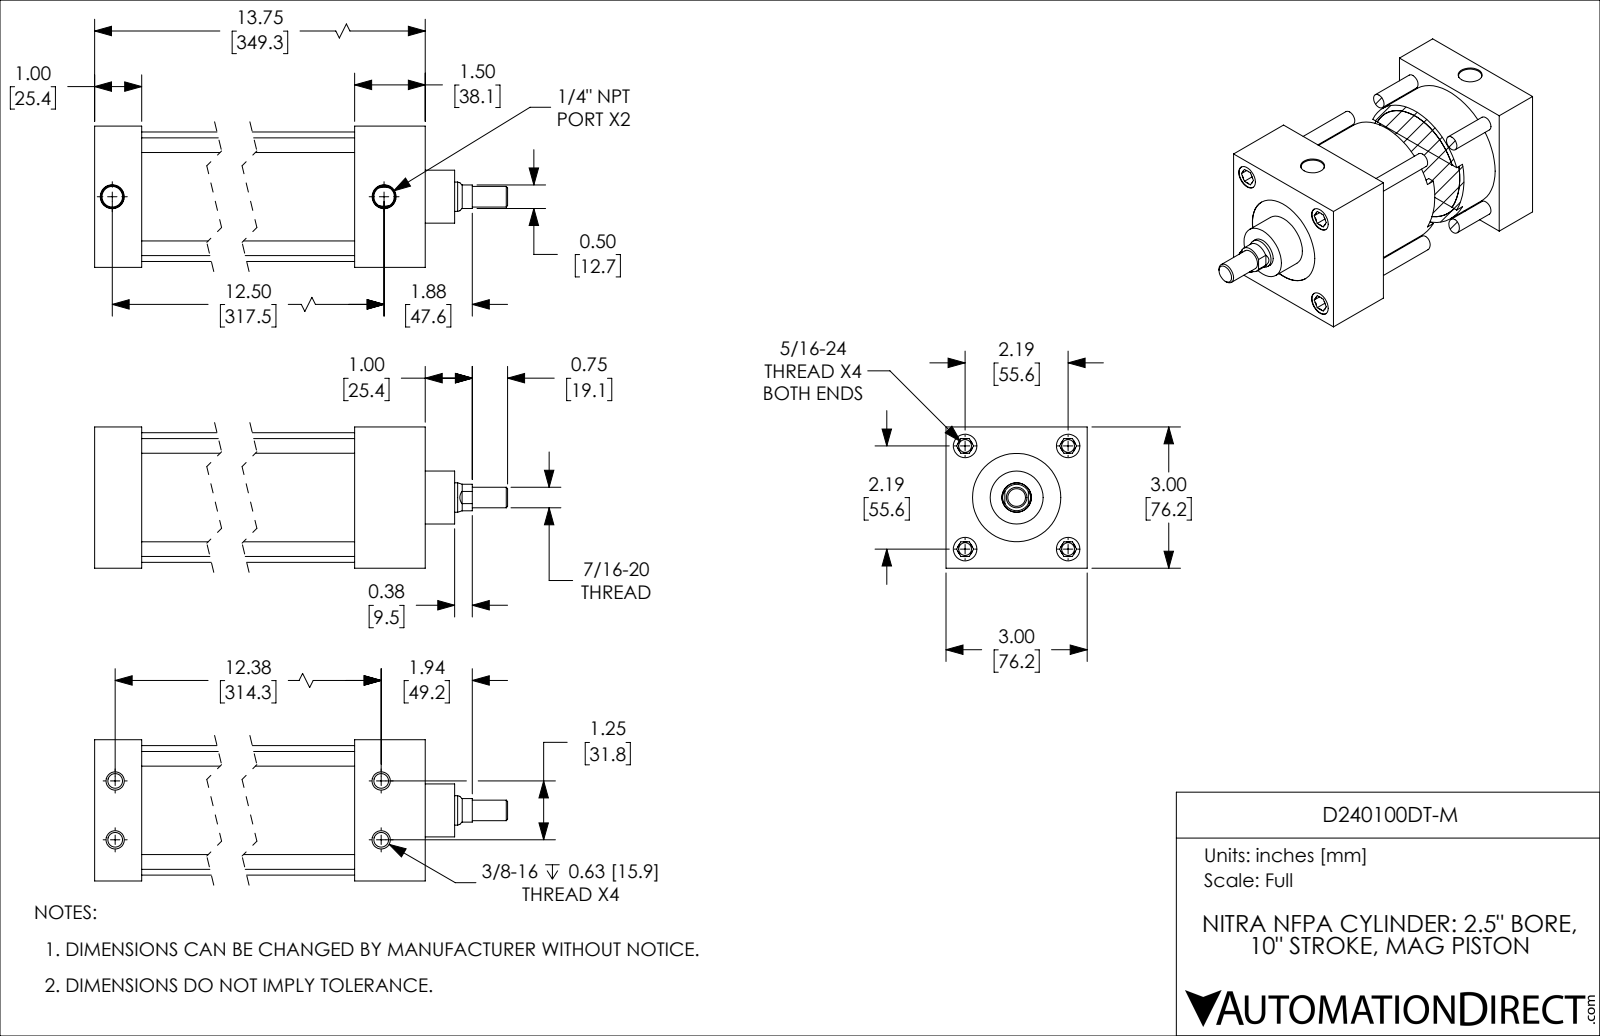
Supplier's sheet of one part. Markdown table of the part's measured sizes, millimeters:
| quantity | value |
| --- | --- |
| part name | D240100DT-M_BODY; D240100DT-M; D240100DT-M_PISTON_KK1 |
| STEP written by | SolidWorks 2019 (CONFIG_CONTROL_DESIGN) |
| units | millimeters |
| bodies | 2 solids, 200 faces (58 planar, 62 cylindrical, 80 other) |
| overall size | 393.7 × 76.2 × 76.2 |
| volume | 761 300 mm³ |
| surface area | 229 700 mm² |
| round holes (diameter × count) | 6.9 × 4, 8 × 4, 12.7 × 4, 11.1 × 2, 15.9 × 1, 47.6 × 1, 63.5 × 1 |
| round bosses / shafts (diameter × count) | 7.9 × 4, 69.9 × 1, 63.5 × 1, 28.6 × 1, 15.8 × 1, 11.1 × 1 |
| partial cylindrical surfaces (radius × count) | 7.1 × 1 |
| main face-to-face distances | 76.2, 25.4, 311.2, 285.8, 349.3, 323.9, 38.1, 31.8, 57.2, 254 |
| hole center spacings | 39.3, 55.6, 316.3, 16, 16, 31.8, 78.7, 314.3 |
